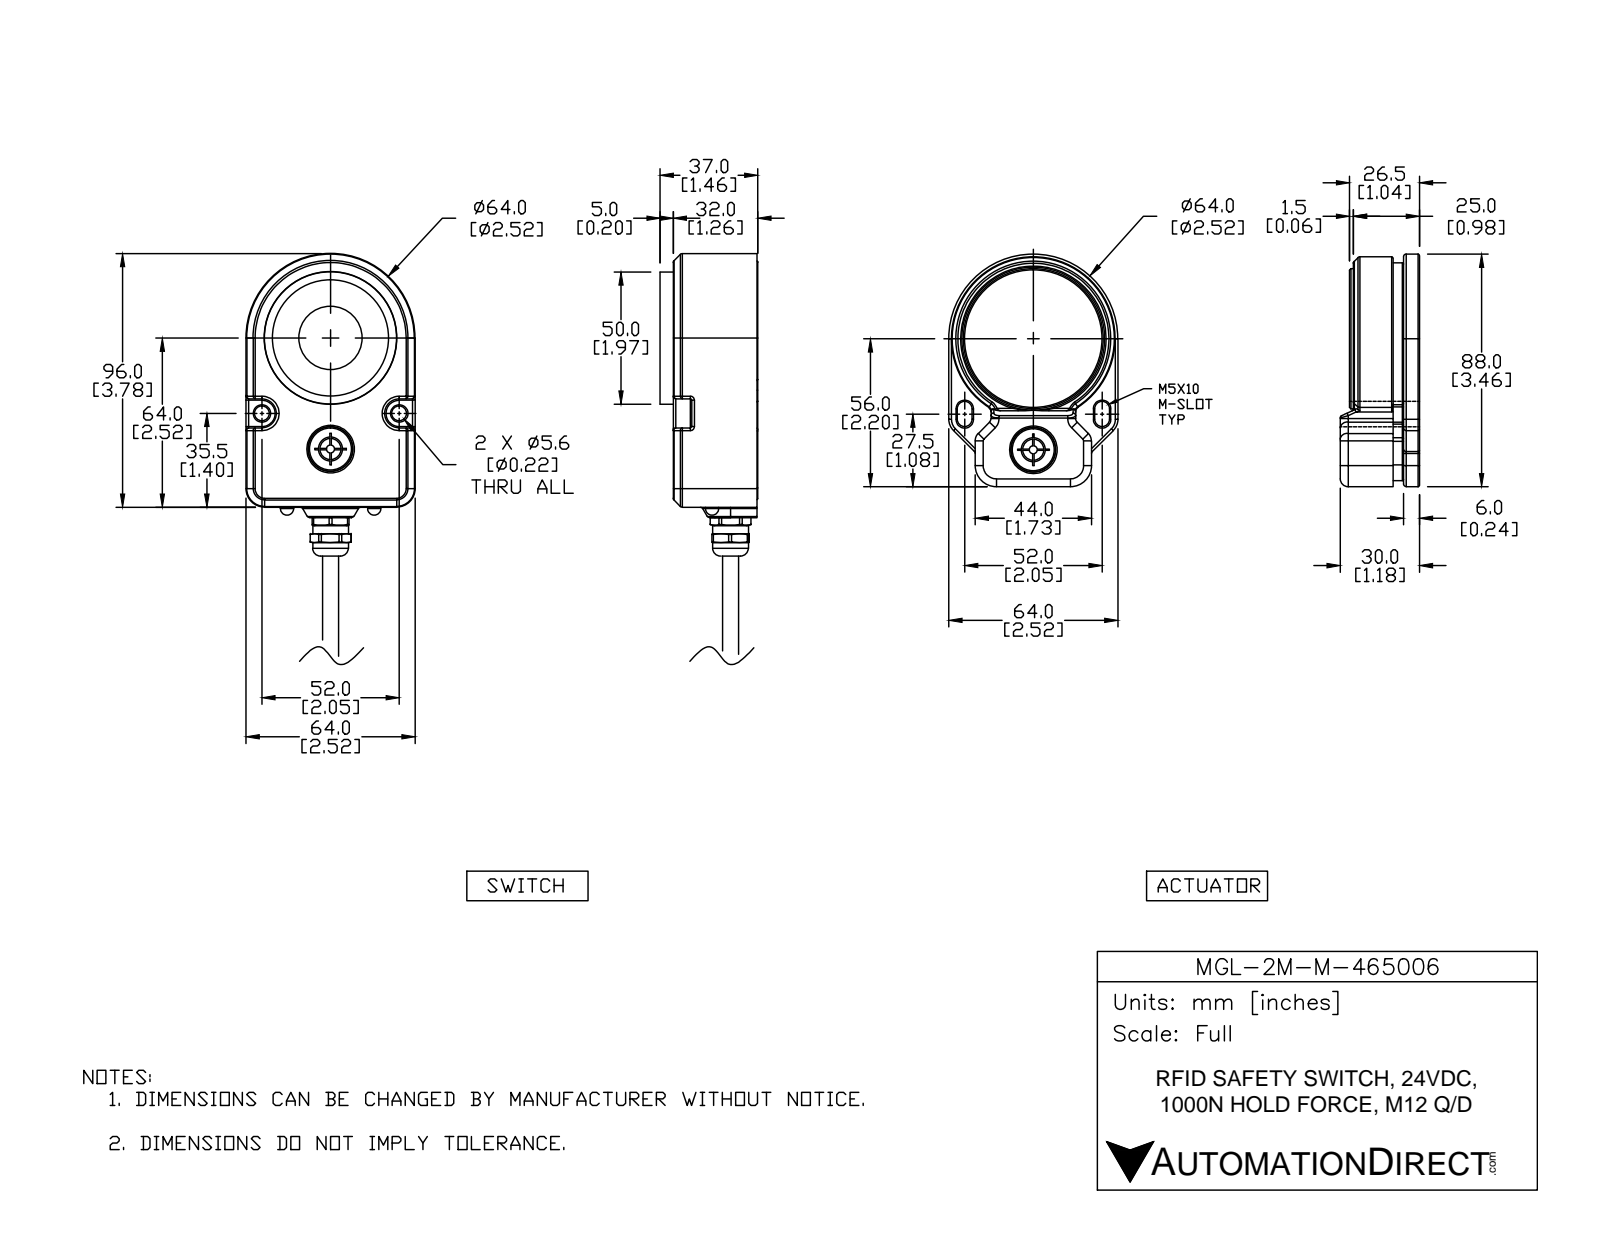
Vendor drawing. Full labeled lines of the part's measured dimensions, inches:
Part name (STEP PRODUCT): MGL-2M-M-465006_1; MGL-2M-M-465006; MGL-2M-M-465006_2
STEP written by: SolidWorks 2017 (AUTOMOTIVE_DESIGN)
Units: inches
Bodies: 20 solids, 1852 faces (454 planar, 786 cylindrical, 612 other)
Overall size (bounding box): 7.717 × 2.539 × 2.52
Volume: 12.42 in³ · Surface area: 169.6 in²
Round holes (diameter × count): ⌀0.098 ×8, ⌀0.157 ×8, ⌀0.13 ×6, ⌀0.315 ×6, ⌀0.197 ×5, ⌀0.323 ×3, ⌀0.22 ×2, ⌀0.354 ×2, ⌀0.374 ×2, ⌀0.413 ×2, ⌀0.669 ×2, ⌀0.252 ×1
Round bosses / shafts (diameter × count): ⌀0.02 ×4, ⌀0.079 ×3, ⌀0.236 ×2, ⌀0.228 ×2, ⌀0.213 ×2, ⌀2.441 ×1, ⌀2.26 ×1, ⌀2.087 ×1
Partial cylindrical surfaces — rounded edges, fillets, slot ends (radius × count): R0.02 ×216, R0.039 ×87, R0.079 ×30, R0.012 ×17, R0.118 ×15, R0.157 ×9, R0.024 ×7, R0.177 ×6
Main face-to-face distances: 0.236, 0.413, 0.118, 0.748, 1.89, 2.303, 1.043, 0.394, 0.354, 1.142
Hole centre spacings: 0.706, 0.768, 1.086, 1.024, 0.346, 0.376, 0.382, 0.384
